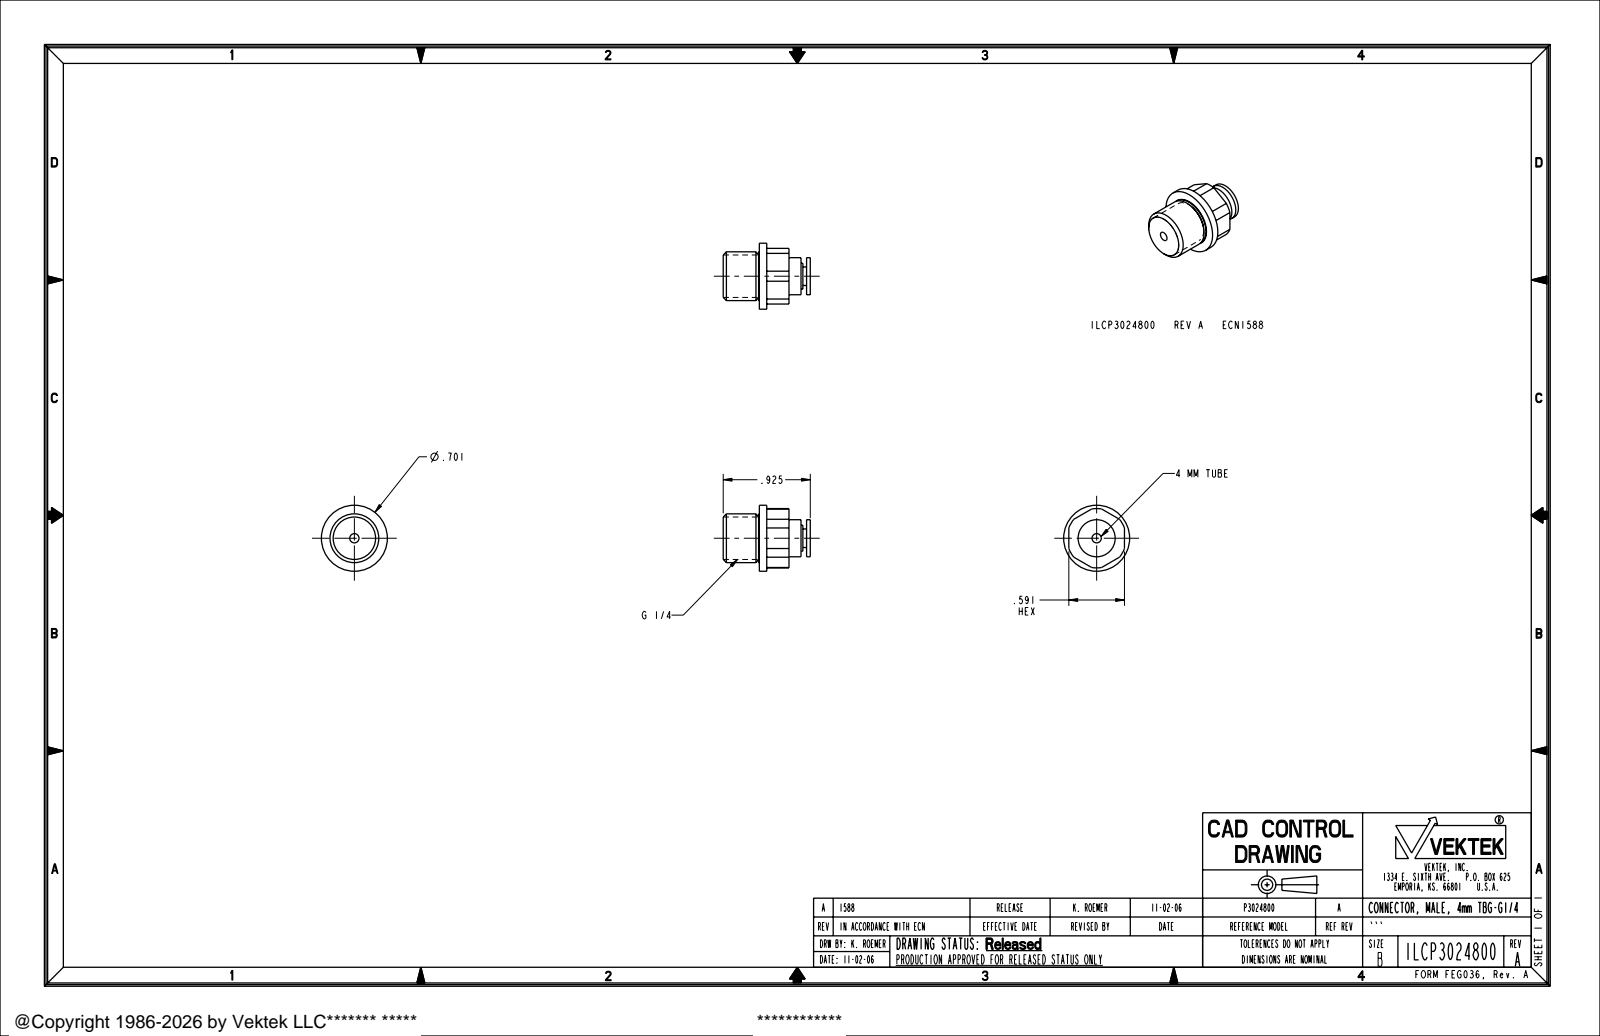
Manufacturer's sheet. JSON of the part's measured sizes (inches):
{"part_name": "ILCP3024800", "step_written_by": "PRO/ENGINEER BY PARAMETRIC TECHNOLOGY CORPORATION, 2005180 (AUTOMOTIVE_DESIGN_CC2)", "units": "inches", "bodies": {"solids": 1, "faces": 47, "planar": 17, "cylindrical": 26, "other": 4}, "overall_size": [0.925, 0.701, 0.701], "volume_in3": 0.197, "surface_area_in2": 3.245, "round_holes": [[0.098, 1]], "round_bosses_or_shafts": [[0.701, 1], [0.518, 1], [0.451, 1], [0.394, 1], [0.276, 1], [0.197, 1]], "partial_cylinders_radius": [[0.315, 1]], "face_to_face_distances": [0.463, 0.384, 0.315, 0.591, 0.699, 0.079, 0.226, 0.541, 0.925, 0.236]}
